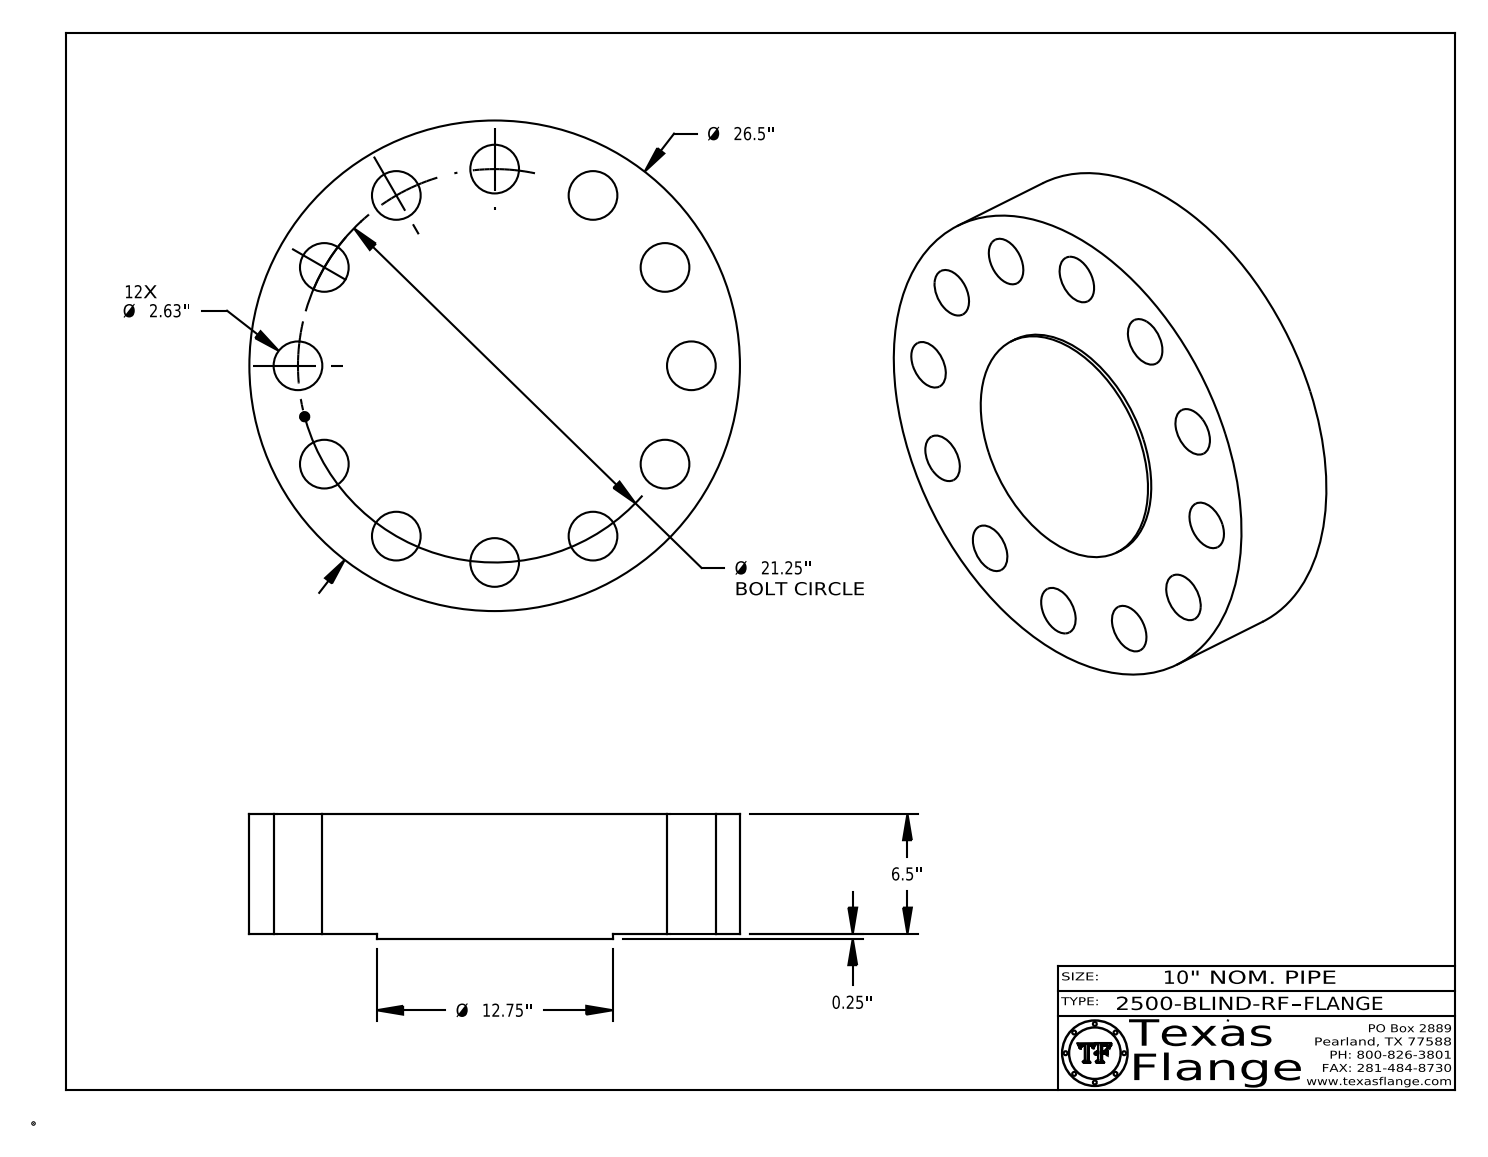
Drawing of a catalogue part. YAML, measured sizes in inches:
part_name: "2500-BLIND-RF"
step_written_by: "CATIA V5 STEP AP214 (AUTOMOTIVE_DESIGN)"
units: inches
bodies: {solids: 1, faces: 416, planar: 368, cylindrical: 48, other: 0}
overall_size: [26.5, 26.5, 6.75]
volume: 3193
surface_area: 2168
round_holes:
  - {diameter: 2.63, count: 12}
  - {diameter: 0.495, count: 1}
round_bosses_or_shafts:
  - {diameter: 0.03, count: 8}
  - {diameter: 26.5, count: 1}
  - {diameter: 12.75, count: 1}
  - {diameter: 0.39, count: 1}
face_to_face_distances: [6.5, 0.25, 6.75, 6.735, 6.485, 0.015, 0.148, 0.144, 0.027, 0.096]
hole_center_spacings: [5.5, 10.625, 18.403, 15.026, 20.526, 15.026, 20.526, 21.25]
